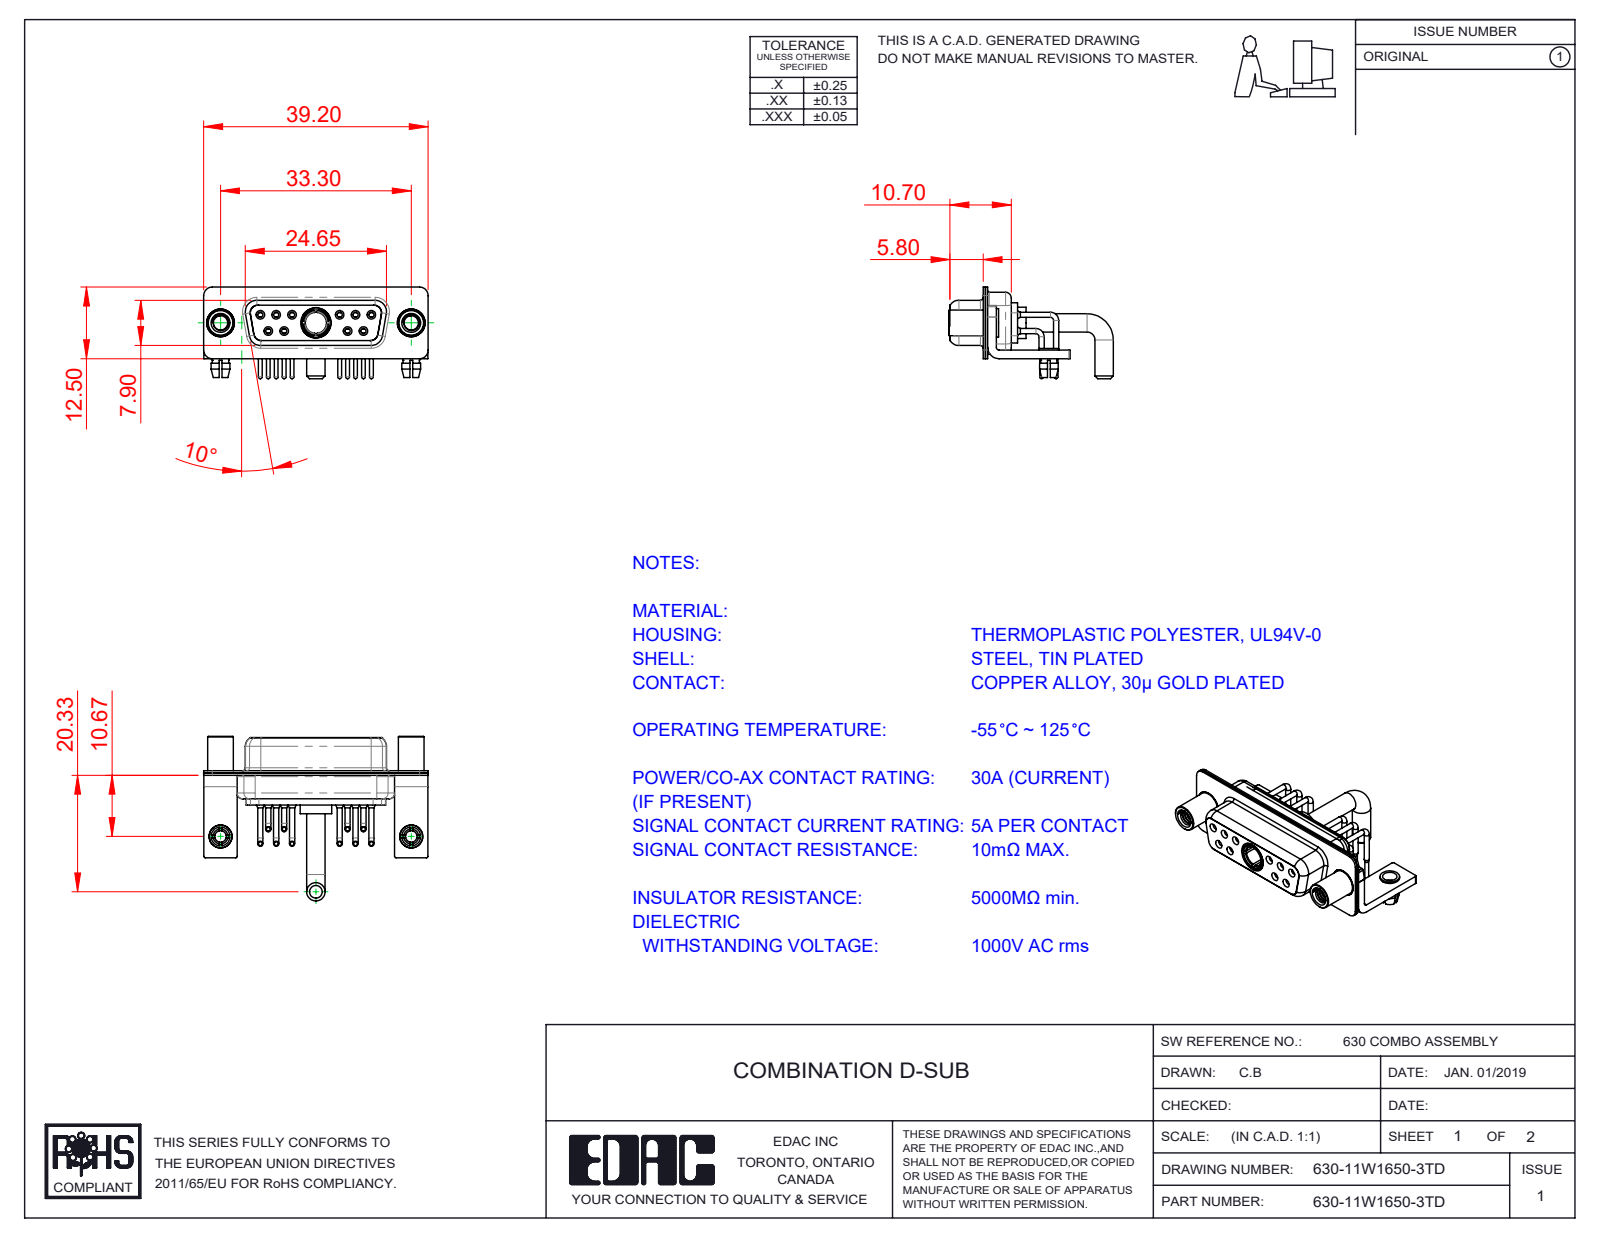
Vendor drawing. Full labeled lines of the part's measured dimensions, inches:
Part name (STEP PRODUCT): 630Combo Stabilizer Bracket; 630Combo Contact Row 1; 630-11W1650-3TD; 630Combo Contact Row 2 (+6 more)
STEP written by: SolidWorks 2020 (CONFIG_CONTROL_DESIGN)
Units: inches
Bodies: 21 solids, 1077 faces (316 planar, 496 cylindrical, 265 other)
Overall size (bounding box): 1.543 × 1.131 × 0.63
Volume: 0.192 in³ · Surface area: 11.62 in²
Round holes (diameter × count): ⌀0.079 ×12, ⌀0.035 ×10, ⌀0.043 ×10, ⌀0.059 ×10, ⌀0.067 ×6, ⌀0.063 ×4, ⌀0.098 ×4, ⌀0.191 ×3, ⌀0.126 ×2, ⌀0.157 ×2, ⌀0.159 ×2, ⌀0.146 ×1
Round bosses / shafts (diameter × count): ⌀0.035 ×10, ⌀0.026 ×10, ⌀0.063 ×6, ⌀0.197 ×2, ⌀0.195 ×2, ⌀0.189 ×2, ⌀0.177 ×2, ⌀0.157 ×2
Partial cylindrical surfaces — rounded edges, fillets, slot ends (radius × count): R0.01 ×16, R0.059 ×16, R0.079 ×13, R0.053 ×12, R0.063 ×8, R0.02 ×5, R0.024 ×4, R0.026 ×4
Main face-to-face distances: 0.016, 0.031, 0.018, 0.055, 0.333, 0.059, 0.071, 0.35, 0.244, 0.091
Hole centre spacings: 0.124, 0.109, 0.545, 0.436, 0.654, 0.198, 0.198, 0.218
